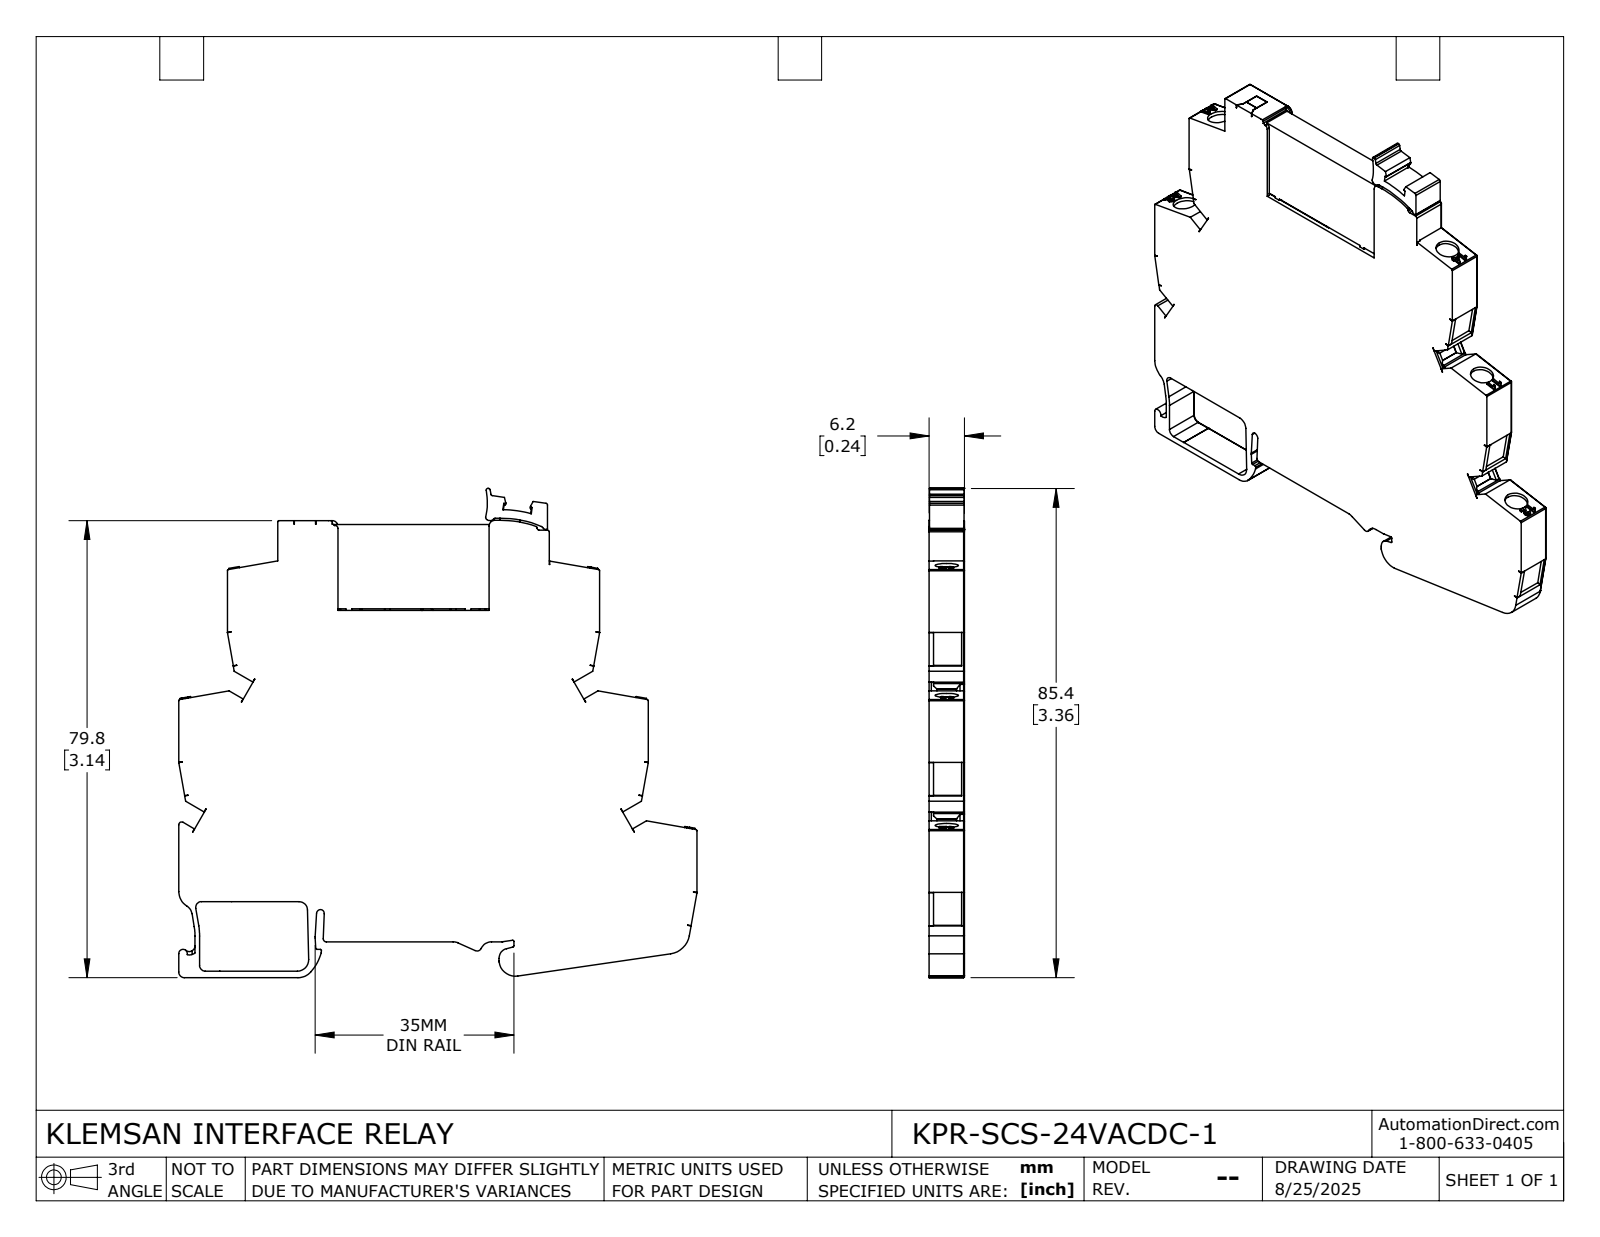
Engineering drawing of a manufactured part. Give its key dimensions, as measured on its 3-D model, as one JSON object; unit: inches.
{"part_name": "KPR-SCS-24VACDC-1", "step_written_by": "SolidWorks 2024 (CONFIG_CONTROL_DESIGN)", "units": "inches", "bodies": {"solids": 1, "faces": 764, "planar": 578, "cylindrical": 148, "other": 38}, "overall_size": [3.563, 3.363, 0.244], "volume_in3": 2.036, "surface_area_in2": 22.6, "round_holes": [[0.159, 5]], "round_bosses_or_shafts": [[0.016, 2]], "partial_cylinders_radius": [[0.008, 22], [0.012, 11], [0.004, 10], [0.039, 9], [0.02, 7], [0.016, 5], [0.035, 5], [0.079, 5]], "face_to_face_distances": [0.244, 0.024, 0.22, 0.197, 0.02, 2.867, 2.288, 0.579, 0.334, 0.335], "hole_center_spacings": [0.484, 0.485, 0.485, 0.969]}
